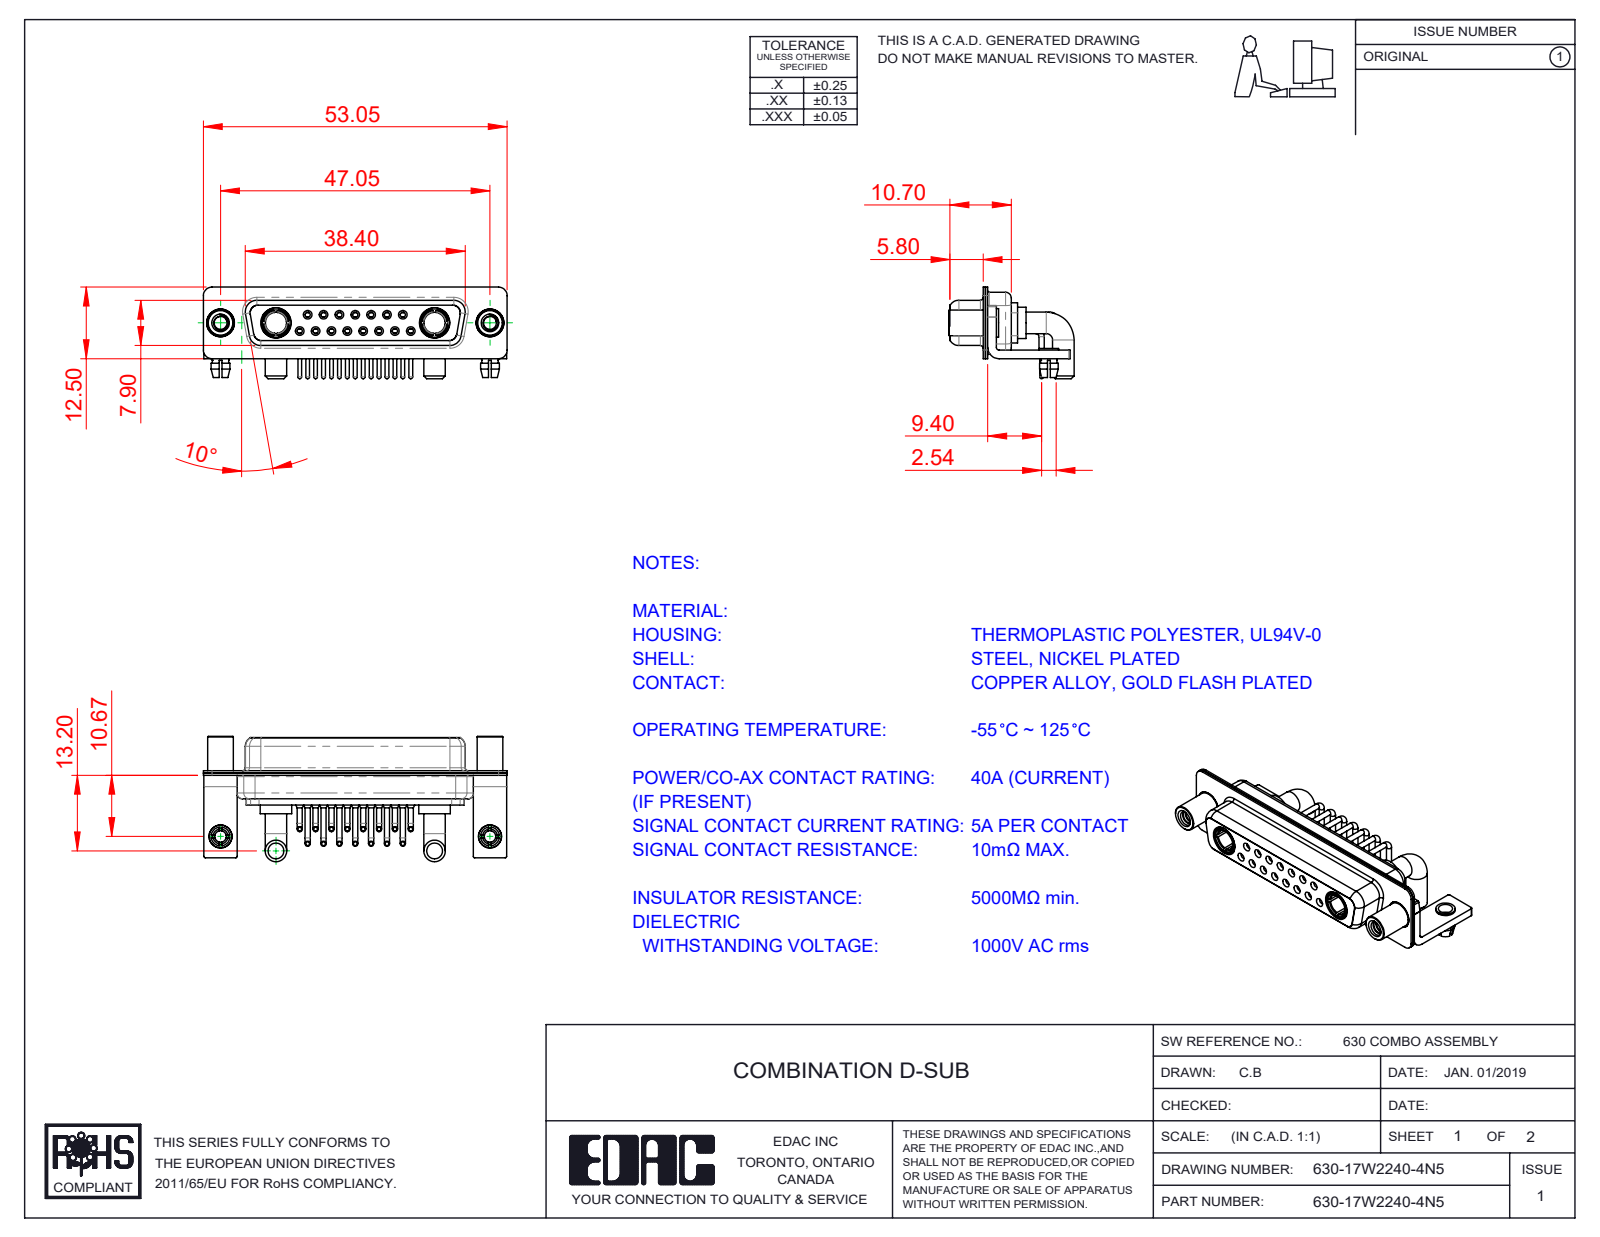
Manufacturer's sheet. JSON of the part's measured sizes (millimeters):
{"part_name": "630Combo Contact Row 1; 630Combo Stabilizer Bracket; 630Combo Threaded Standoff_5; Power Socket_40A RA (+6 more)", "step_written_by": "SolidWorks 2020 (CONFIG_CONTROL_DESIGN)", "units": "millimeters", "bodies": {"solids": 28, "faces": 1410, "planar": 420, "cylindrical": 624, "other": 366}, "overall_size": [53.05, 21.88, 16], "volume_mm3": 4603, "surface_area_mm2": 10389, "round_holes": [[2, 17], [0.9, 15], [1.1, 15], [1.5, 15], [1.6, 8], [1.7, 7], [4.85, 4], [2.26, 2], [2.5, 2], [3.2, 2], [3.7, 2], [4, 2]], "round_bosses_or_shafts": [[0.9, 15], [0.65, 15], [1.6, 7], [3.75, 4], [5.5, 2], [5.2, 2], [5, 2], [4.96, 2]], "partial_cylinders_radius": [[0.25, 16], [1.5, 16], [2, 13], [1.35, 8], [1.6, 8], [0.5, 5], [0.6, 4], [0.65, 4]], "face_to_face_distances": [0.4, 0.45, 1.4, 8.45, 1.8, 0.8, 8.9, 6.2, 7.05, 1.5], "hole_center_spacings": [3.16, 2.77, 5.54, 8.31, 5.04, 7.49, 11.08, 5.03]}
